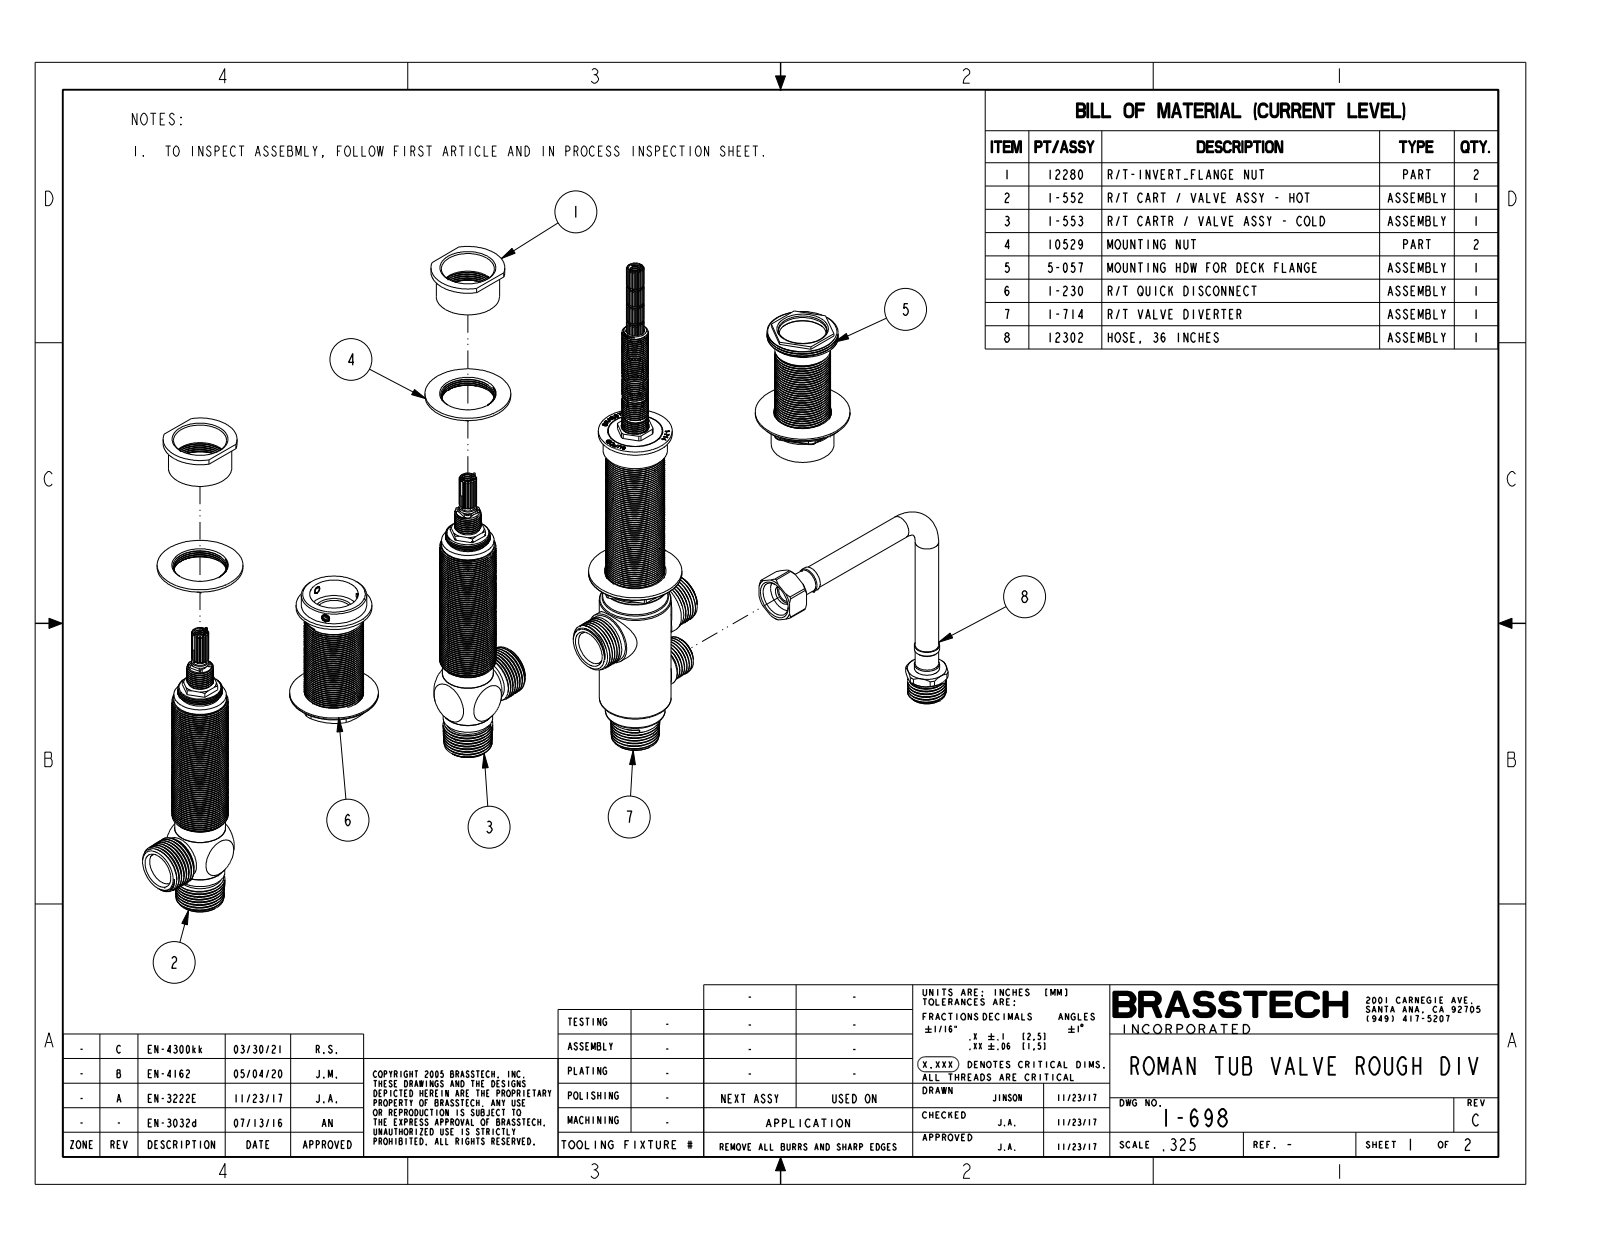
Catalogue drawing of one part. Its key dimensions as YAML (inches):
part_name: "1-698"
step_written_by: "CREO PARAMETRIC BY PTC INC, 2018400 (AUTOMOTIVE_DESIGN)"
units: inches
bodies: {solids: 10, faces: 3641, planar: 925, cylindrical: 1533, other: 1183}
overall_size: [20.415, 15.404, 2]
volume: 15.85
surface_area: 302.1
round_holes:
  - {diameter: 0.196, count: 2}
  - {diameter: 0.201, count: 2}
  - {diameter: 0.236, count: 2}
  - {diameter: 0.276, count: 2}
  - {diameter: 0.77, count: 2}
  - {diameter: 1.025, count: 2}
  - {diameter: 1.12, count: 2}
  - {diameter: 1.18, count: 2}
  - {diameter: 0.136, count: 1}
  - {diameter: 0.138, count: 1}
  - {diameter: 0.202, count: 1}
  - {diameter: 0.274, count: 1}
round_bosses_or_shafts:
  - {diameter: 0.043, count: 4}
  - {diameter: 1.811, count: 2}
  - {diameter: 1.335, count: 2}
  - {diameter: 1.187, count: 2}
  - {diameter: 1.11, count: 2}
  - {diameter: 1.075, count: 2}
  - {diameter: 1.047, count: 2}
  - {diameter: 0.945, count: 2}
partial_cylinders:
  - {radius: 0.04, count: 14}
  - {radius: 0.08, count: 8}
  - {radius: 0.039, count: 6}
  - {radius: 0.15, count: 6}
  - {radius: 0.164, count: 3}
  - {radius: 0.26, count: 2}
  - {radius: 0.3, count: 2}
  - {radius: 0.775, count: 2}
face_to_face_distances: [0.061, 0.27, 3.15, 2.31, 1.22, 1.93, 1.281, 3.211, 3.937, 0.339]
hole_center_spacings: [4, 5, 0.703, 2.192, 5.703, 8, 9, 10]
